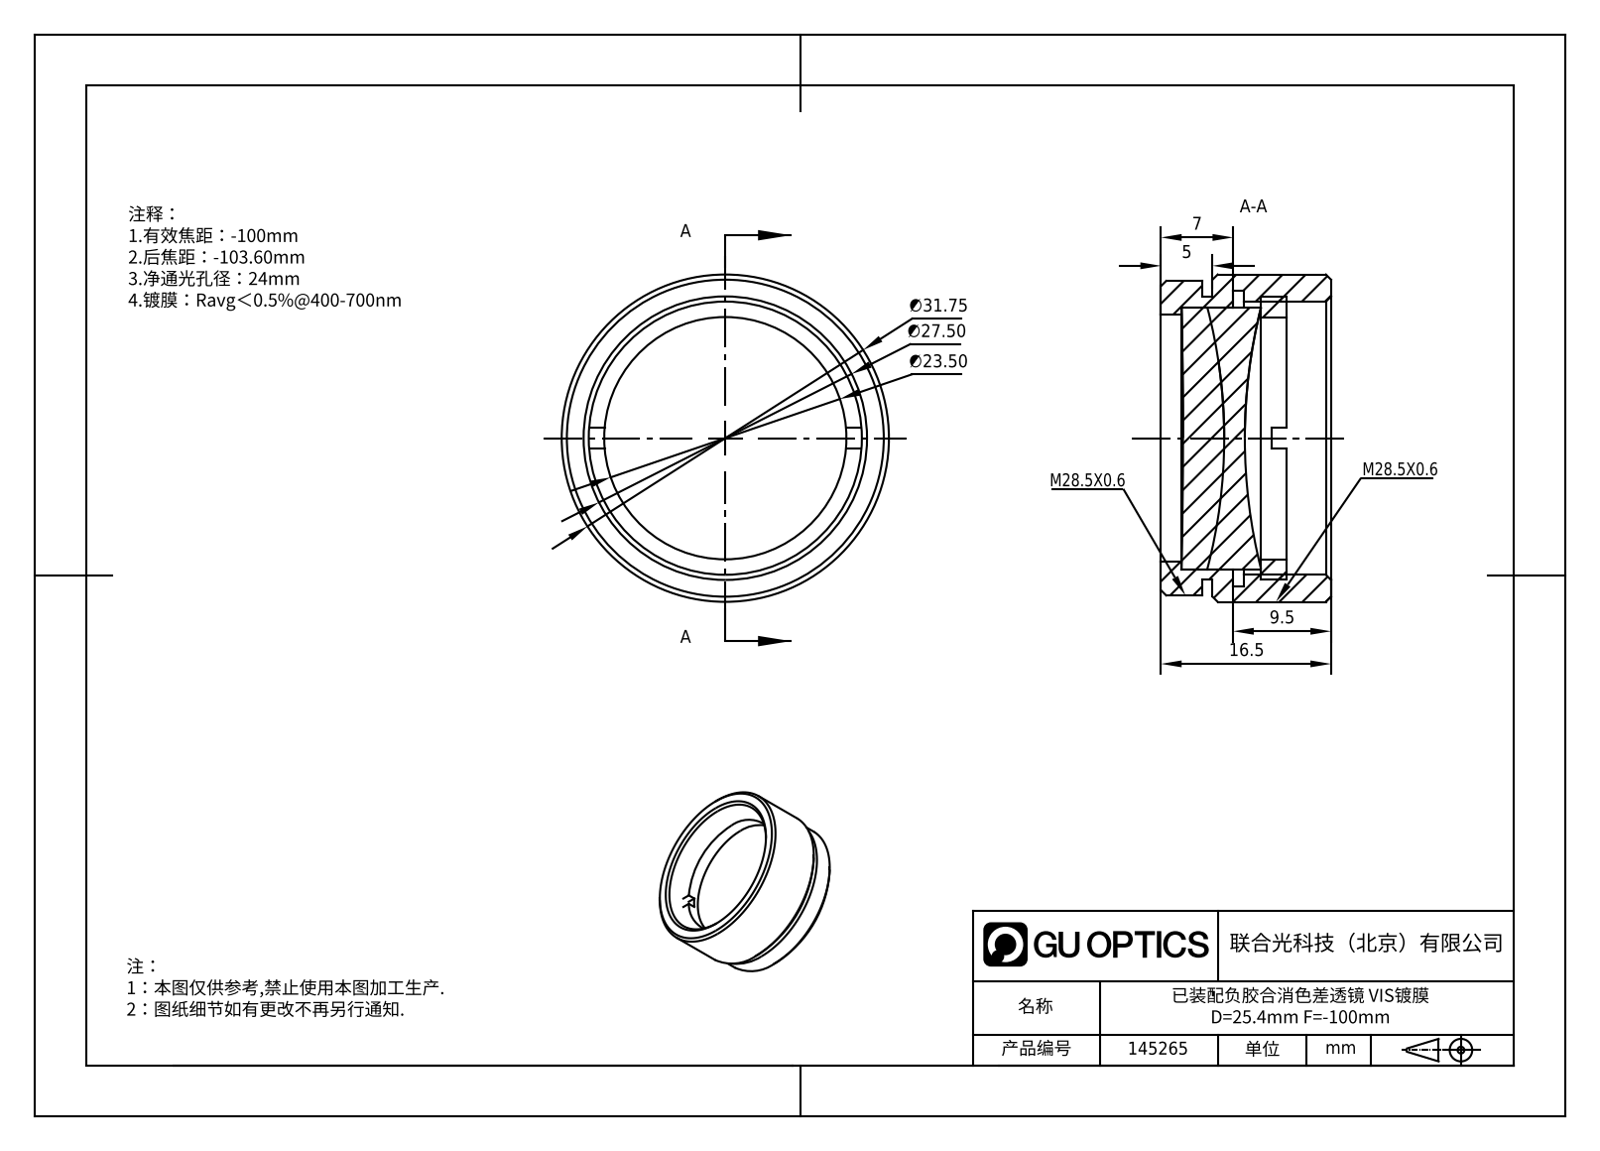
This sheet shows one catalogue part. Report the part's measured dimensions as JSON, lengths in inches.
{"part_name": "145265", "step_written_by": "SolidWorks 2020 (CONFIG_CONTROL_DESIGN)", "units": "inches", "bodies": {"solids": 4, "faces": 54, "planar": 16, "cylindrical": 22, "other": 16}, "overall_size": [1.25, 1.25, 0.65], "volume_in3": 0.468, "surface_area_in2": 11.44, "round_holes": [[0.925, 1], [0.945, 1], [1.043, 1], [1.13, 1]], "round_bosses_or_shafts": [[1.25, 1], [1.201, 1], [1.083, 1], [1, 1]], "face_to_face_distances": [0.118, 0.079, 0.039, 0.157, 0.197, 0.382, 0.481, 0.098, 0.65, 0.267]}
